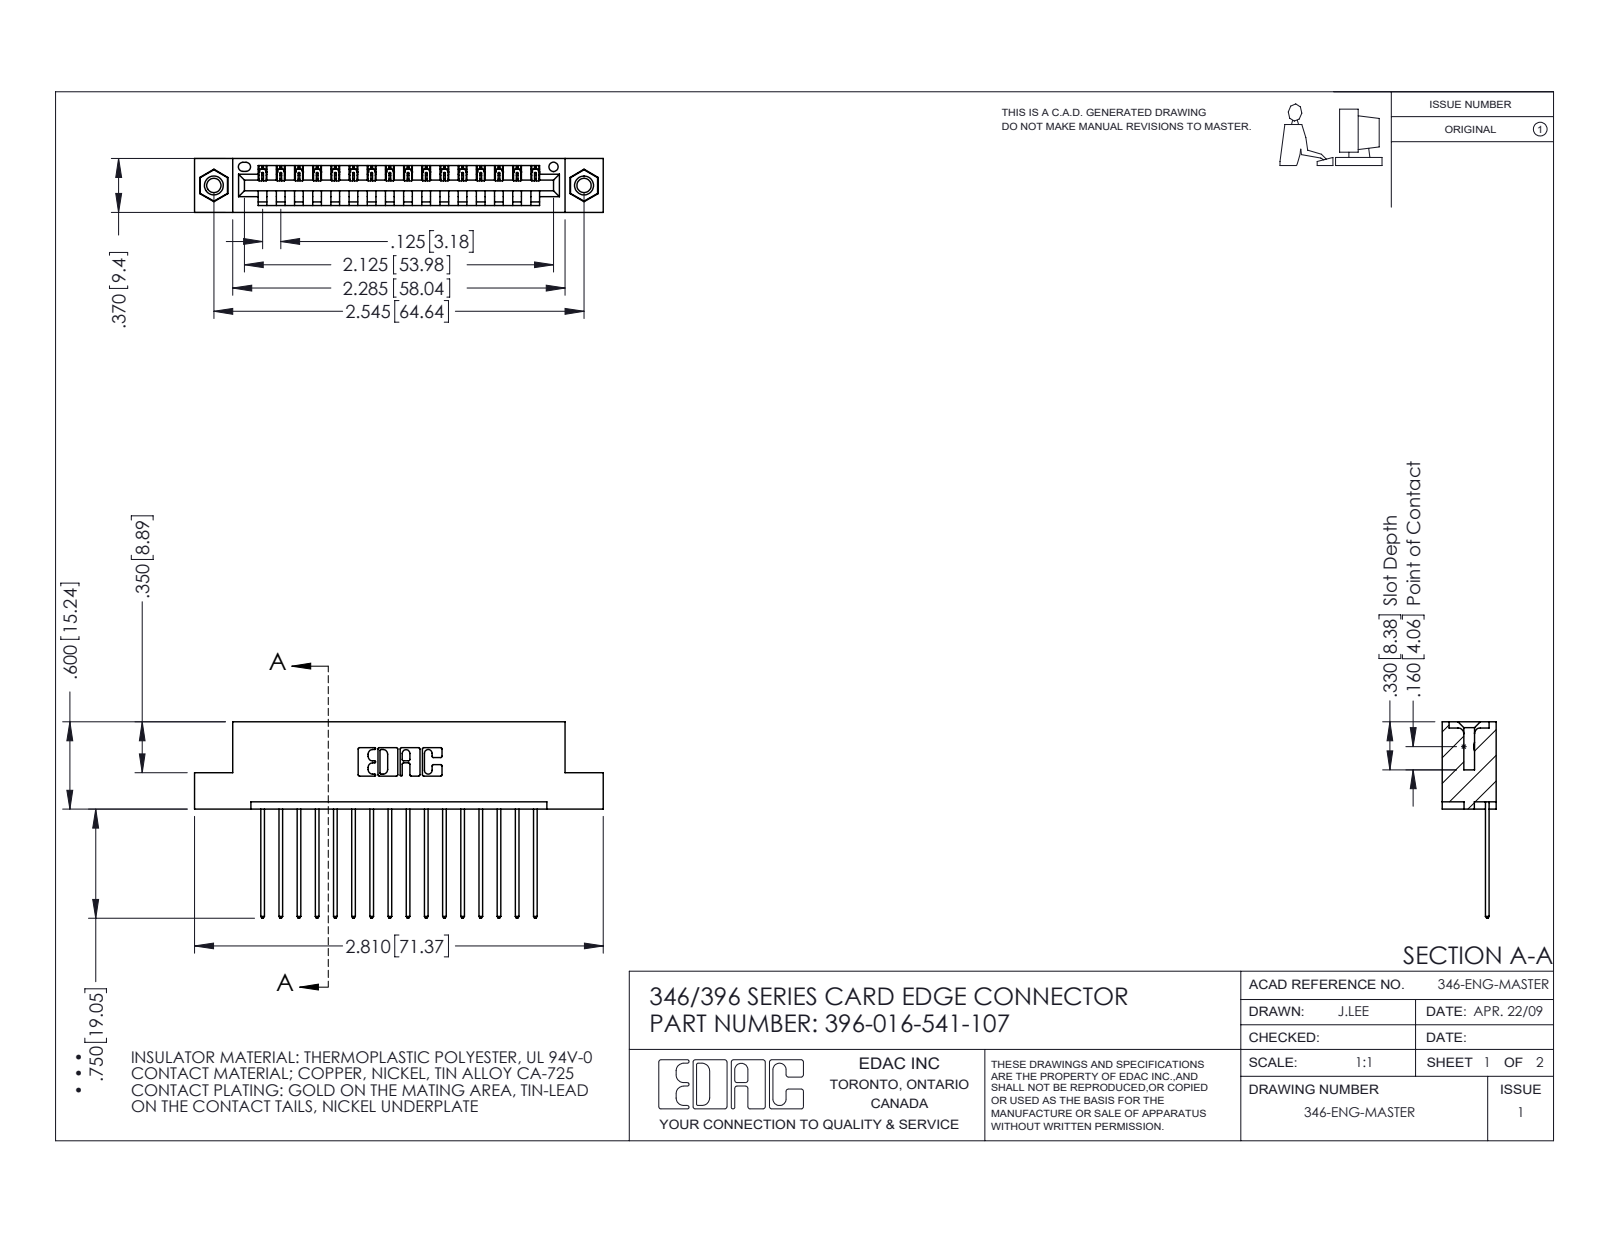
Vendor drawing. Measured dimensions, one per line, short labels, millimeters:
name: 346 Part_Flush Mounting Lugs - 0.156 Dia-TI; 396-016-541-107; 345-250-001_345-250-005-103; 345-292-001_345-293-141
written by: SolidWorks 2016 (CONFIG_CONTROL_DESIGN)
unit: mm
bodies: 19 solids, 1110 faces (748 planar, 346 cylindrical, 16 other)
size: 71.4 × 34.3 × 9.4
volume: 6 690 mm³; area: 8 432 mm²
holes: 2× ⌀2.5, 2× ⌀3.2, 2× ⌀4, 1× ⌀1.6
bosses: 2× ⌀3.9
rounds: 32× R0.2, 32× R0.3, 22× R0.3, 6× R0.2, 6× R0.8, 3× R0.7, 2× R0.8, 2× R1
face distances: 1.2, 8.2, 6.4, 9.4, 1.8, 7.6, 0.6, 3.8, 5.6, 2.5
hole spacings: 6.2, 59.4, 64.6
